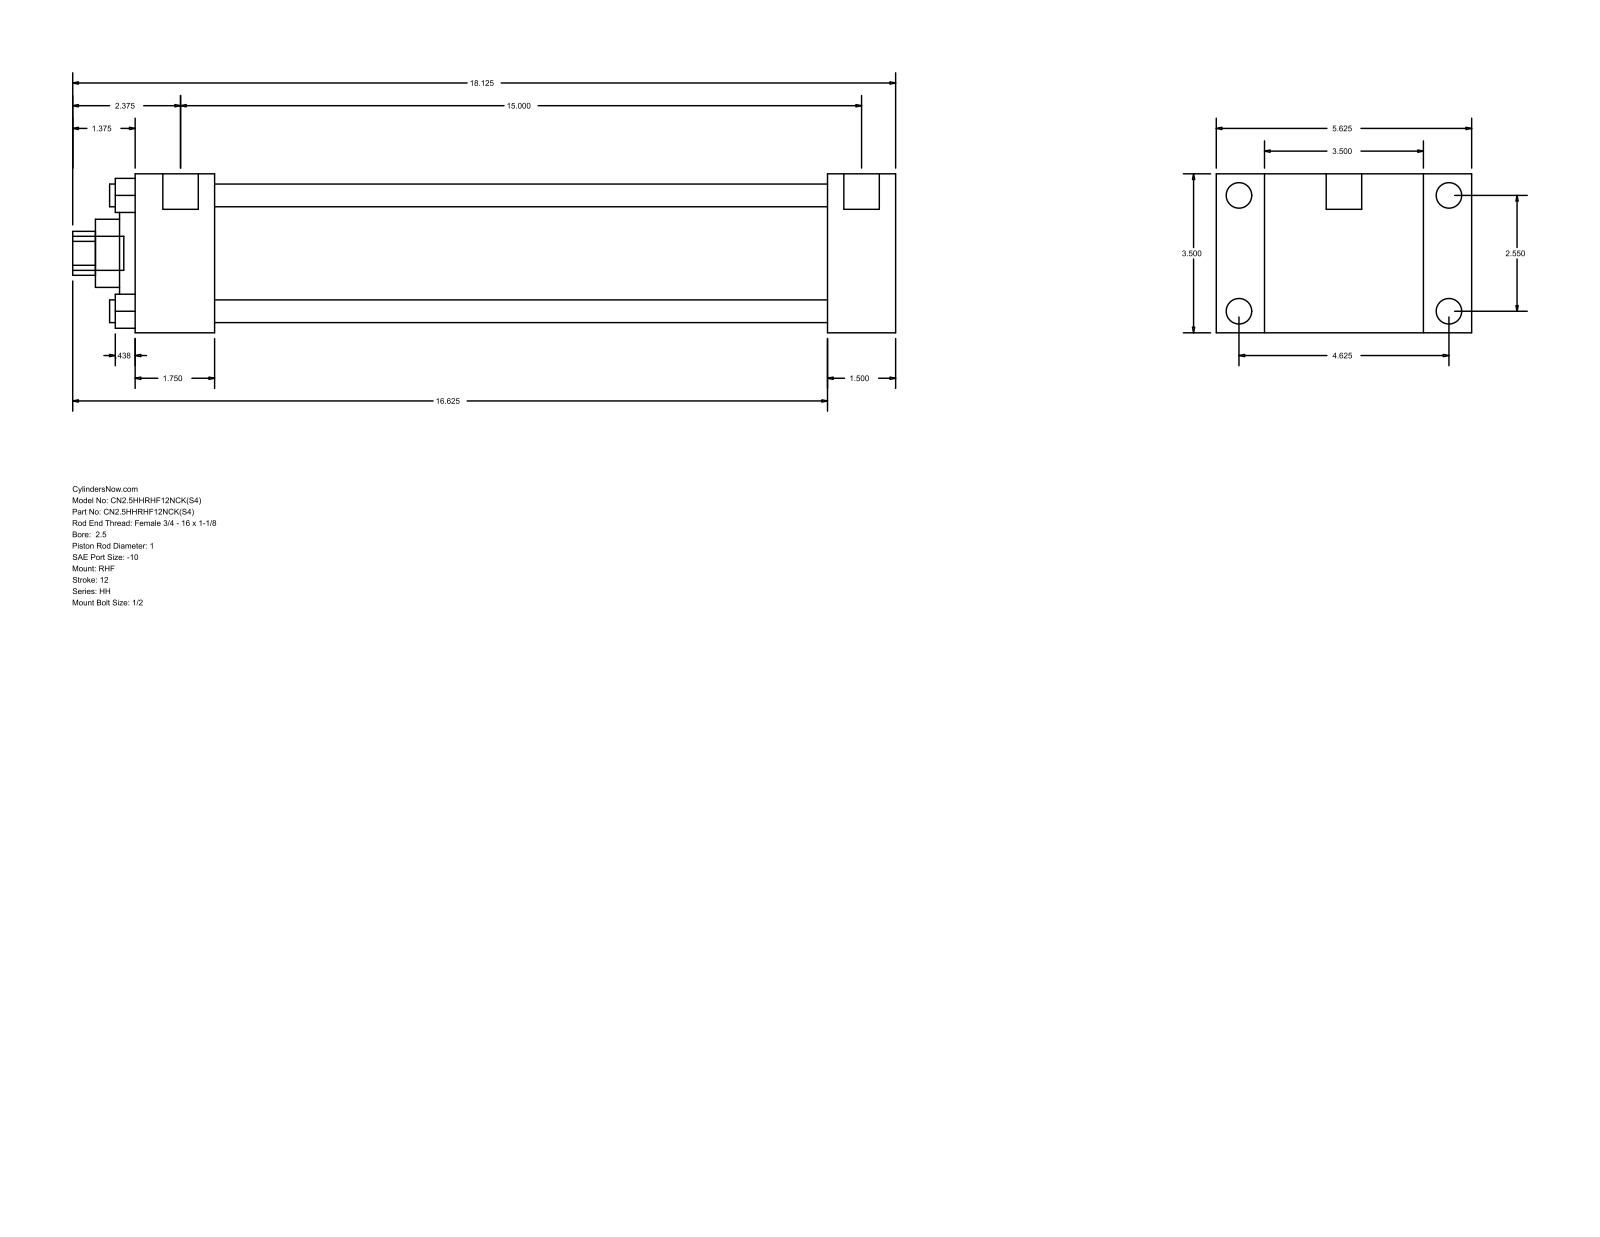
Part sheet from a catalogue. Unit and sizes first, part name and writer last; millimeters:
Units: millimetres
Overall size (bounding box): 460.38 × 142.88 × 88.9
Round holes (diameter × count): ⌀12.7 ×4, ⌀25.4 ×1, ⌀38.1 ×1, ⌀60.33 ×1, ⌀73.03 ×1
Round bosses / shafts (diameter × count): ⌀14.3 ×4, ⌀5.56 ×4, ⌀19.84 ×2, ⌀19.05 ×1
Partial cylindrical surfaces — rounded edges, fillets, slot ends (radius × count): R12.29 ×1
Main face-to-face distances: 88.9, 38.11, 26.99, 115.89, 387.35, 425.46, 142.88, 44.46, 342.89, 381
Hole centre spacings: 45.79, 64.76, 91.58
Bodies: 0 solids, 90 faces (61 planar, 29 cylindrical, 0 other)
Part name (STEP PRODUCT): HH_RHF__0250_1
STEP written by: GSSL Pune (CONFIG_CONTROL_DESIGN)
